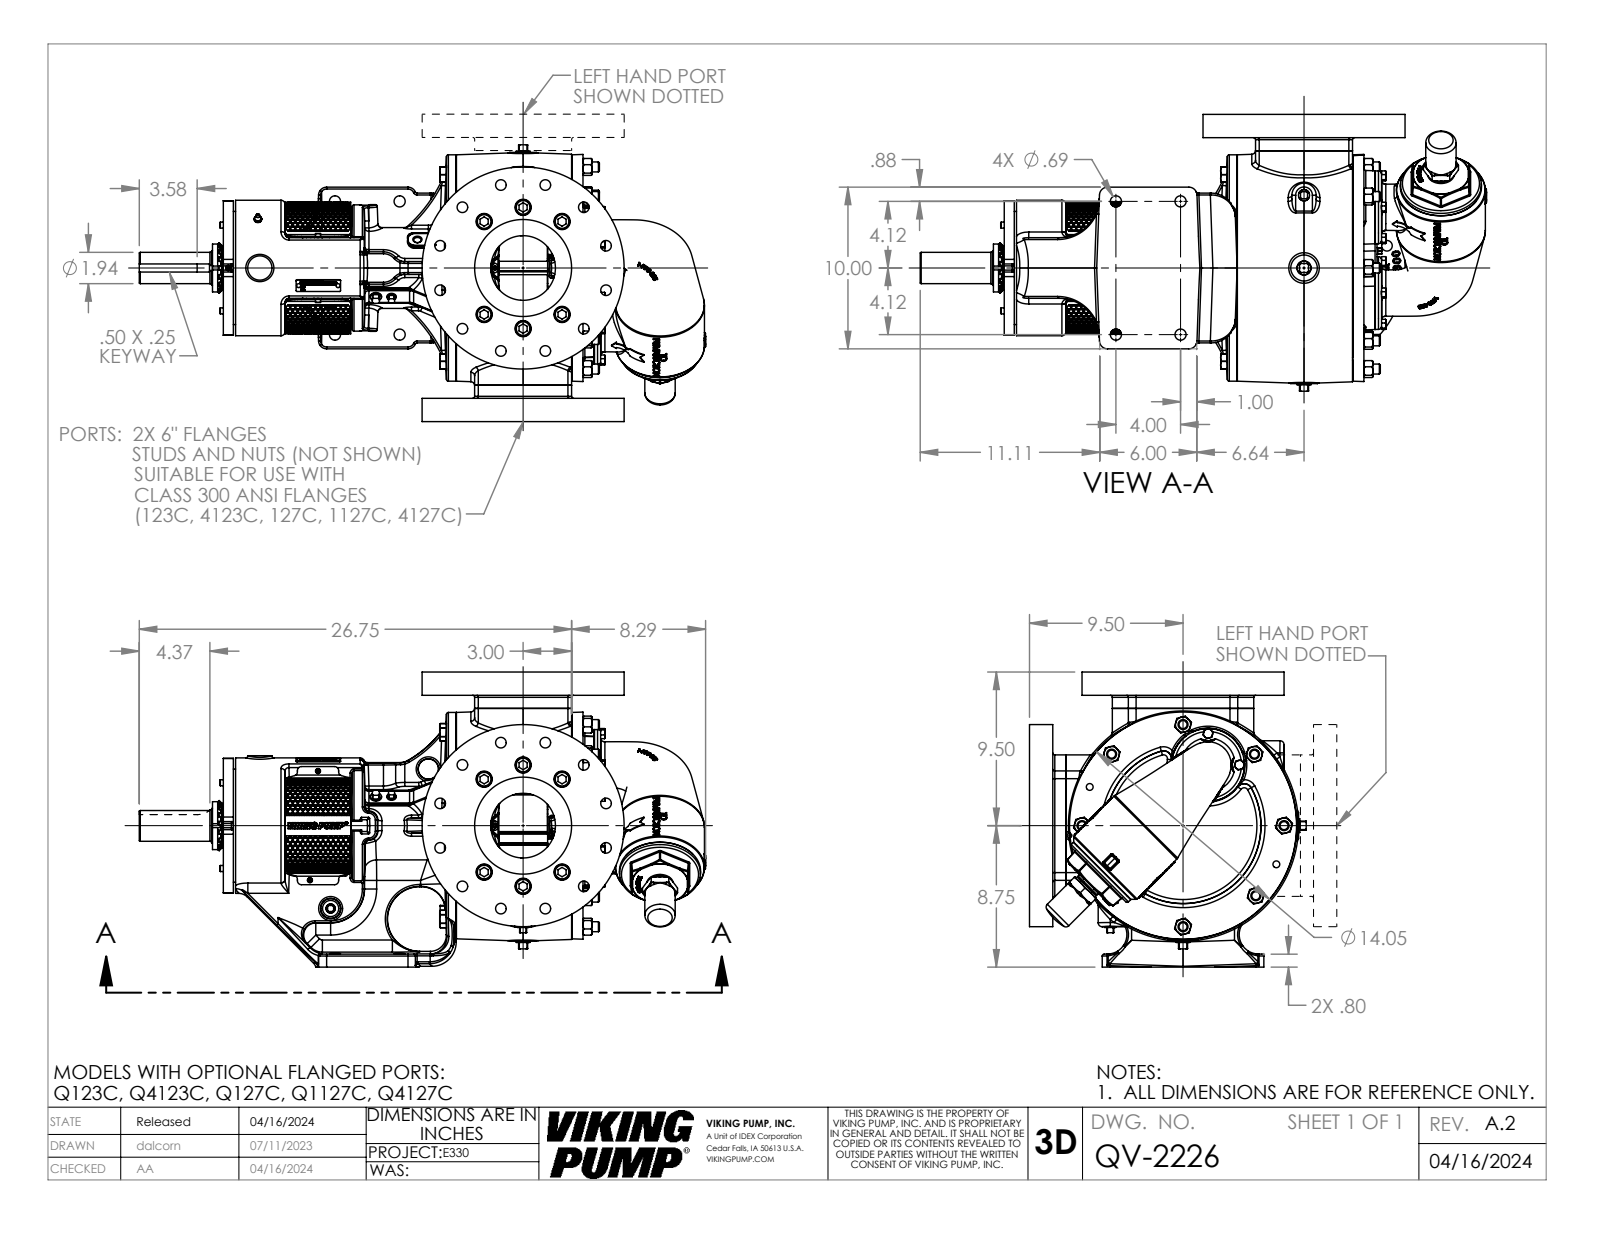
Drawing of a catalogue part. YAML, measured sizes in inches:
part_name: "QV-2226"
step_written_by: "SolidWorks 2022 (AUTOMOTIVE_DESIGN)"
units: inches
bodies: {solids: 1, faces: 4918, planar: 1715, cylindrical: 868, other: 2335}
overall_size: [35.04, 18.25, 17.121]
volume: 2527
surface_area: 2757
round_holes:
  - {diameter: 0.656, count: 36}
  - {diameter: 1, count: 12}
  - {diameter: 0.25, count: 9}
  - {diameter: 0.266, count: 8}
  - {diameter: 0.406, count: 8}
  - {diameter: 0.41, count: 8}
  - {diameter: 1.157, count: 8}
  - {diameter: 0.688, count: 4}
  - {diameter: 0.159, count: 2}
  - {diameter: 0.313, count: 2}
  - {diameter: 0.33, count: 2}
  - {diameter: 0.422, count: 2}
round_bosses_or_shafts:
  - {diameter: 0.937, count: 12}
  - {diameter: 0.625, count: 9}
  - {diameter: 0.617, count: 8}
  - {diameter: 0.375, count: 8}
  - {diameter: 0.625, count: 3}
  - {diameter: 0.312, count: 3}
  - {diameter: 0.19, count: 3}
  - {diameter: 12.5, count: 2}
partial_cylinders:
  - {radius: 0.12, count: 60}
  - {radius: 0.06, count: 34}
  - {radius: 0.25, count: 30}
  - {radius: 0.5, count: 23}
  - {radius: 0.015, count: 18}
  - {radius: 0.092, count: 18}
  - {radius: 0.07, count: 16}
  - {radius: 0.75, count: 16}
face_to_face_distances: [1.44, 16.81, 18.25, 3.75, 0.5, 21.754, 22.254, 2.25, 18.004, 18.504]
hole_center_spacings: [5.313, 10.263, 3.75, 2.75, 9.202, 2.079, 7.513, 1.61]
